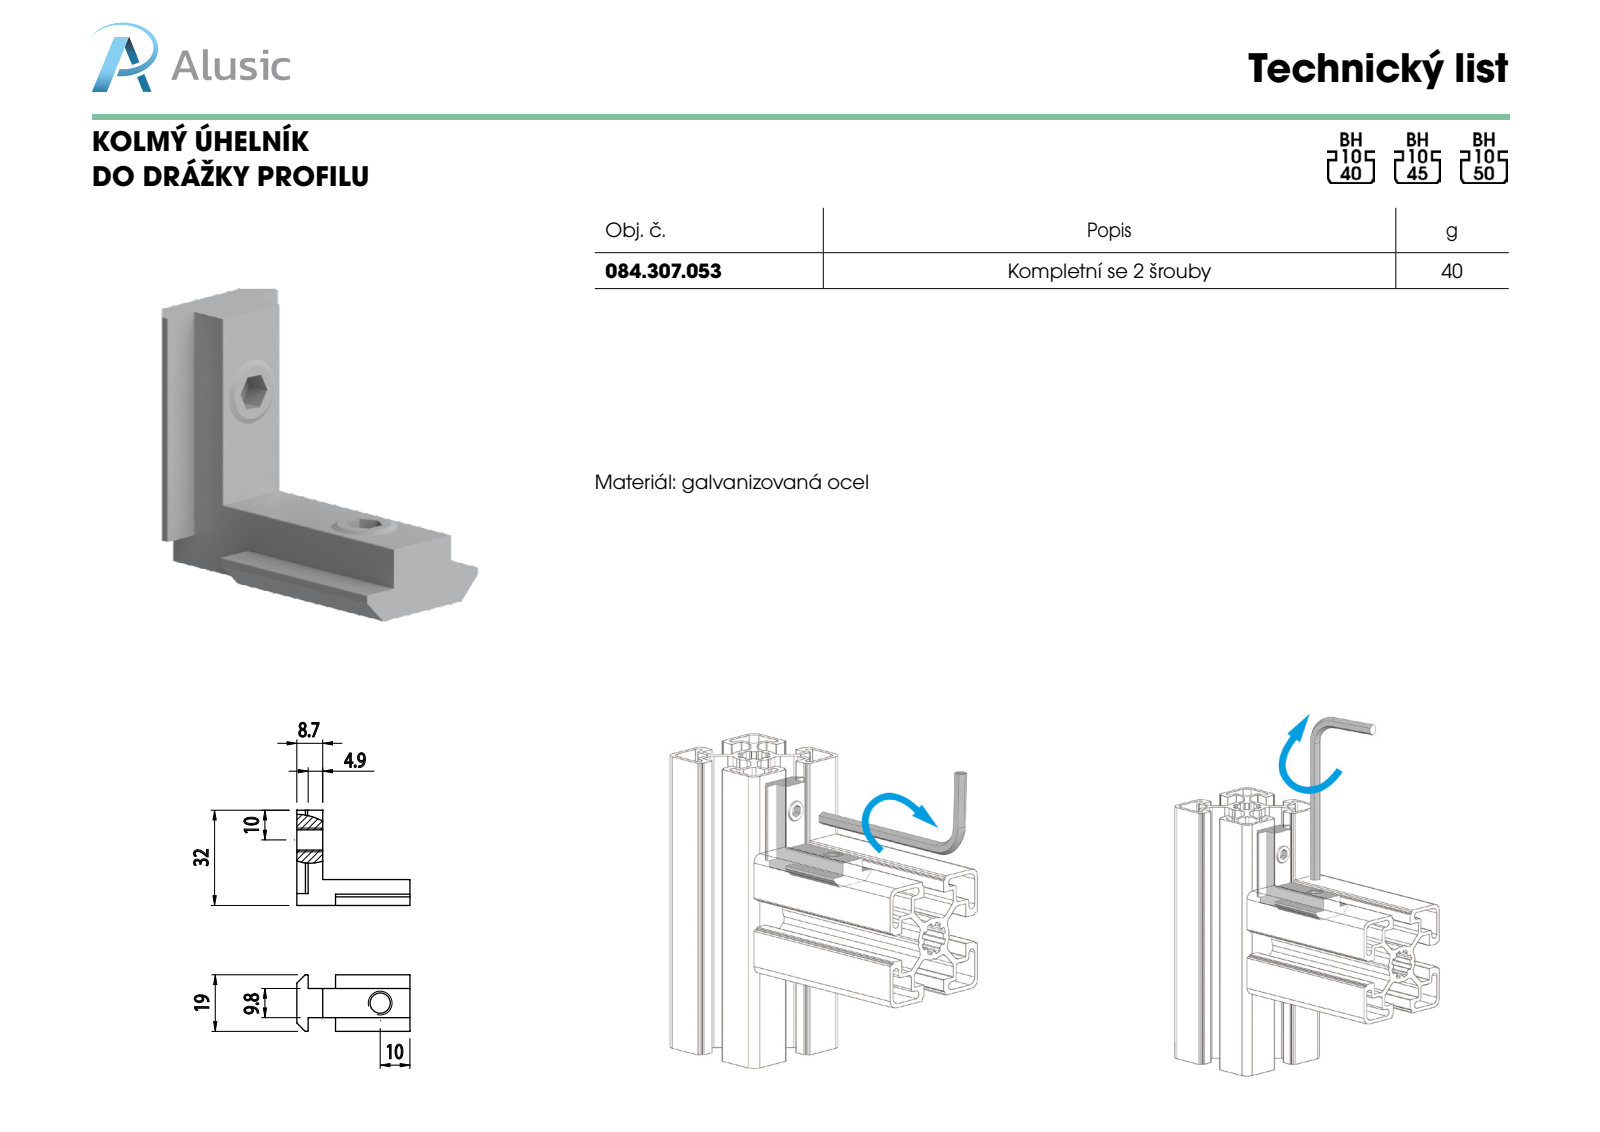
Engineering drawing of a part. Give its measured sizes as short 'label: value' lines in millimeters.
name: 084.307.053
written by: SolidWorks 2012 (CONFIG_CONTROL_DESIGN)
unit: mm
bodies: 1 solid, 48 faces (24 planar, 24 cylindrical, 0 other)
size: 38 × 32 × 19
volume: 6 030 mm³; area: 3 552 mm²
holes: 2× ⌀6.8
rounds: 20× R0.2
face distances: 3.8, 8.7, 4.9, 9.8, 29.3, 34.2, 38, 32, 28.2, 23.3
